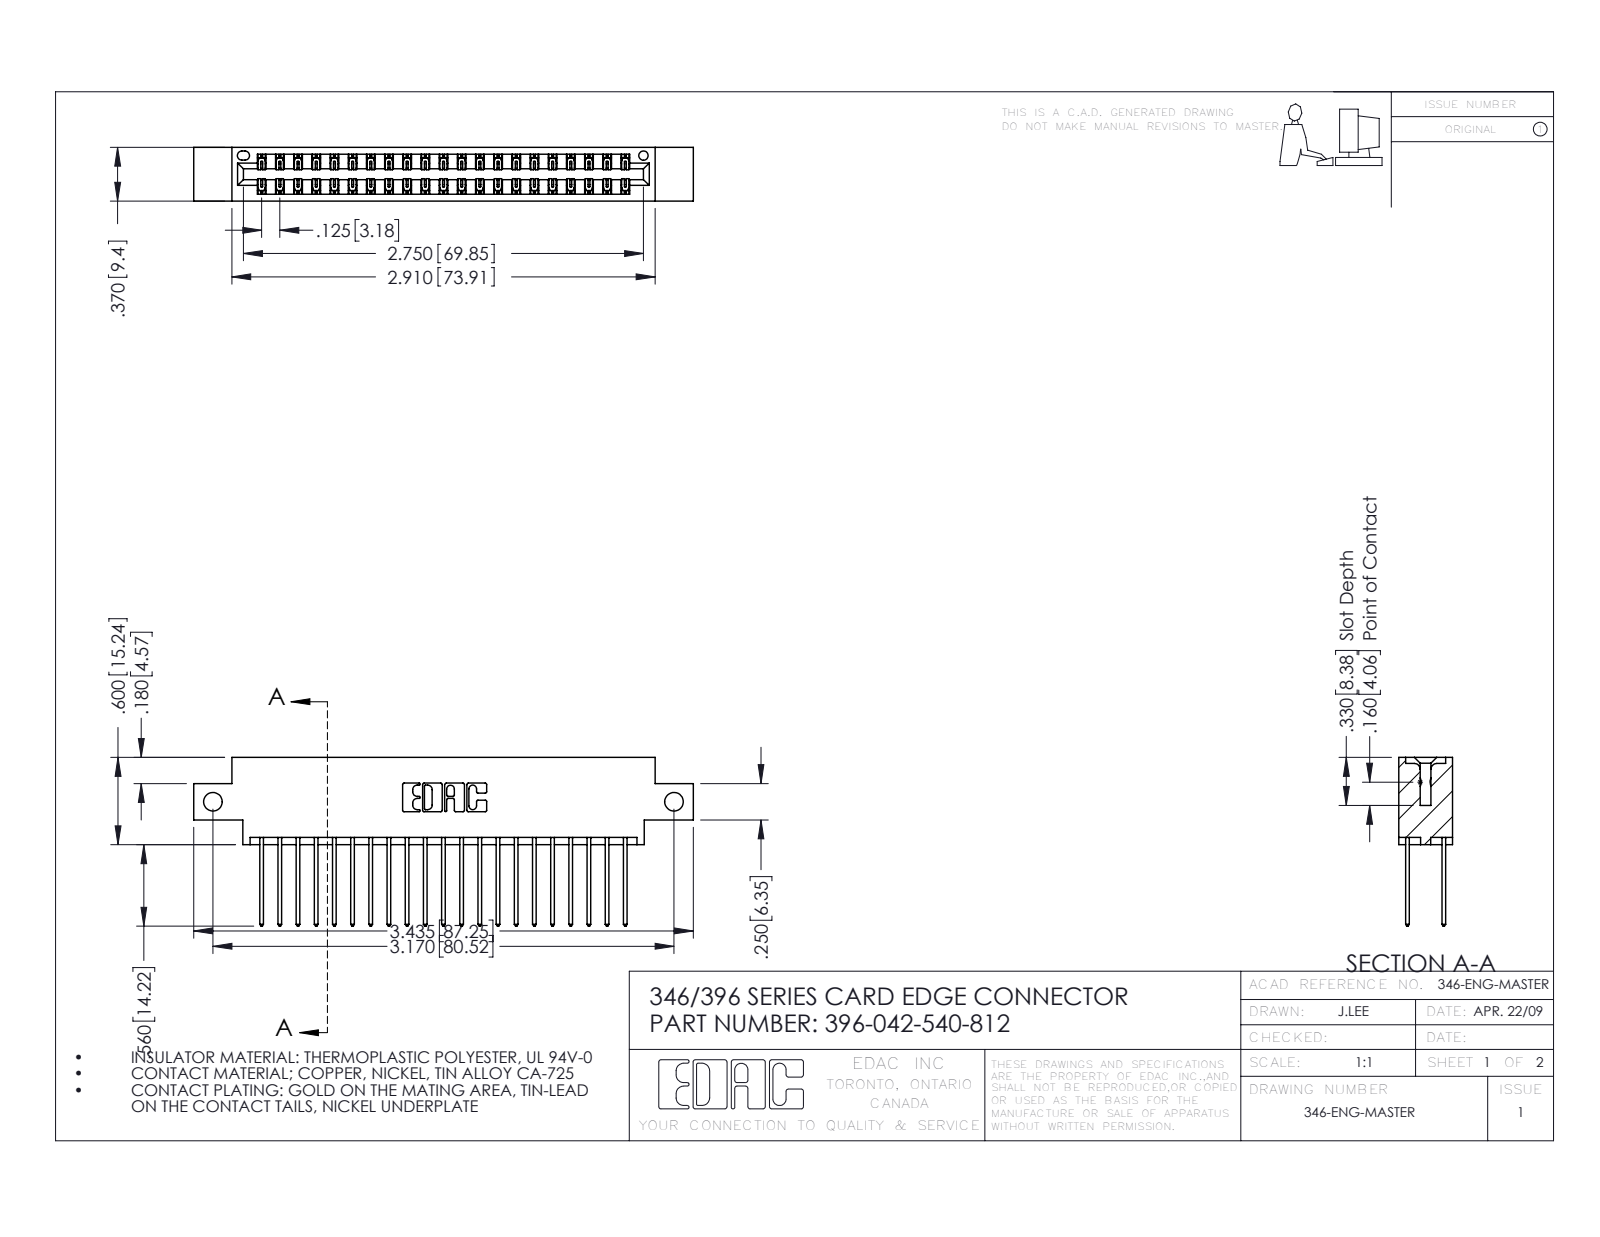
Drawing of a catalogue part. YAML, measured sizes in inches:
part_name: "345-292-001_345-293-140; 346 Part_0.170 Offset - Side Mount; 396-042-540-812"
step_written_by: "SolidWorks 2016 (CONFIG_CONTROL_DESIGN)"
units: inches
bodies: {solids: 43, faces: 2310, planar: 1550, cylindrical: 760, other: 0}
overall_size: [3.435, 1.16, 0.37]
volume: 0.504
surface_area: 18.32
round_holes:
  - {diameter: 0.128, count: 2}
  - {diameter: 0.064, count: 1}
partial_cylinders:
  - {radius: 0.006, count: 63}
  - {radius: 0.01, count: 42}
  - {radius: 0.01, count: 22}
  - {radius: 0.007, count: 6}
  - {radius: 0.031, count: 6}
  - {radius: 0.026, count: 3}
  - {radius: 0.014, count: 2}
  - {radius: 0.022, count: 2}
face_to_face_distances: [0.048, 0.322, 0.25, 0.37, 0.072, 0.298, 0.025, 0.275, 0.148, 0.222]
hole_center_spacings: [3.17]
